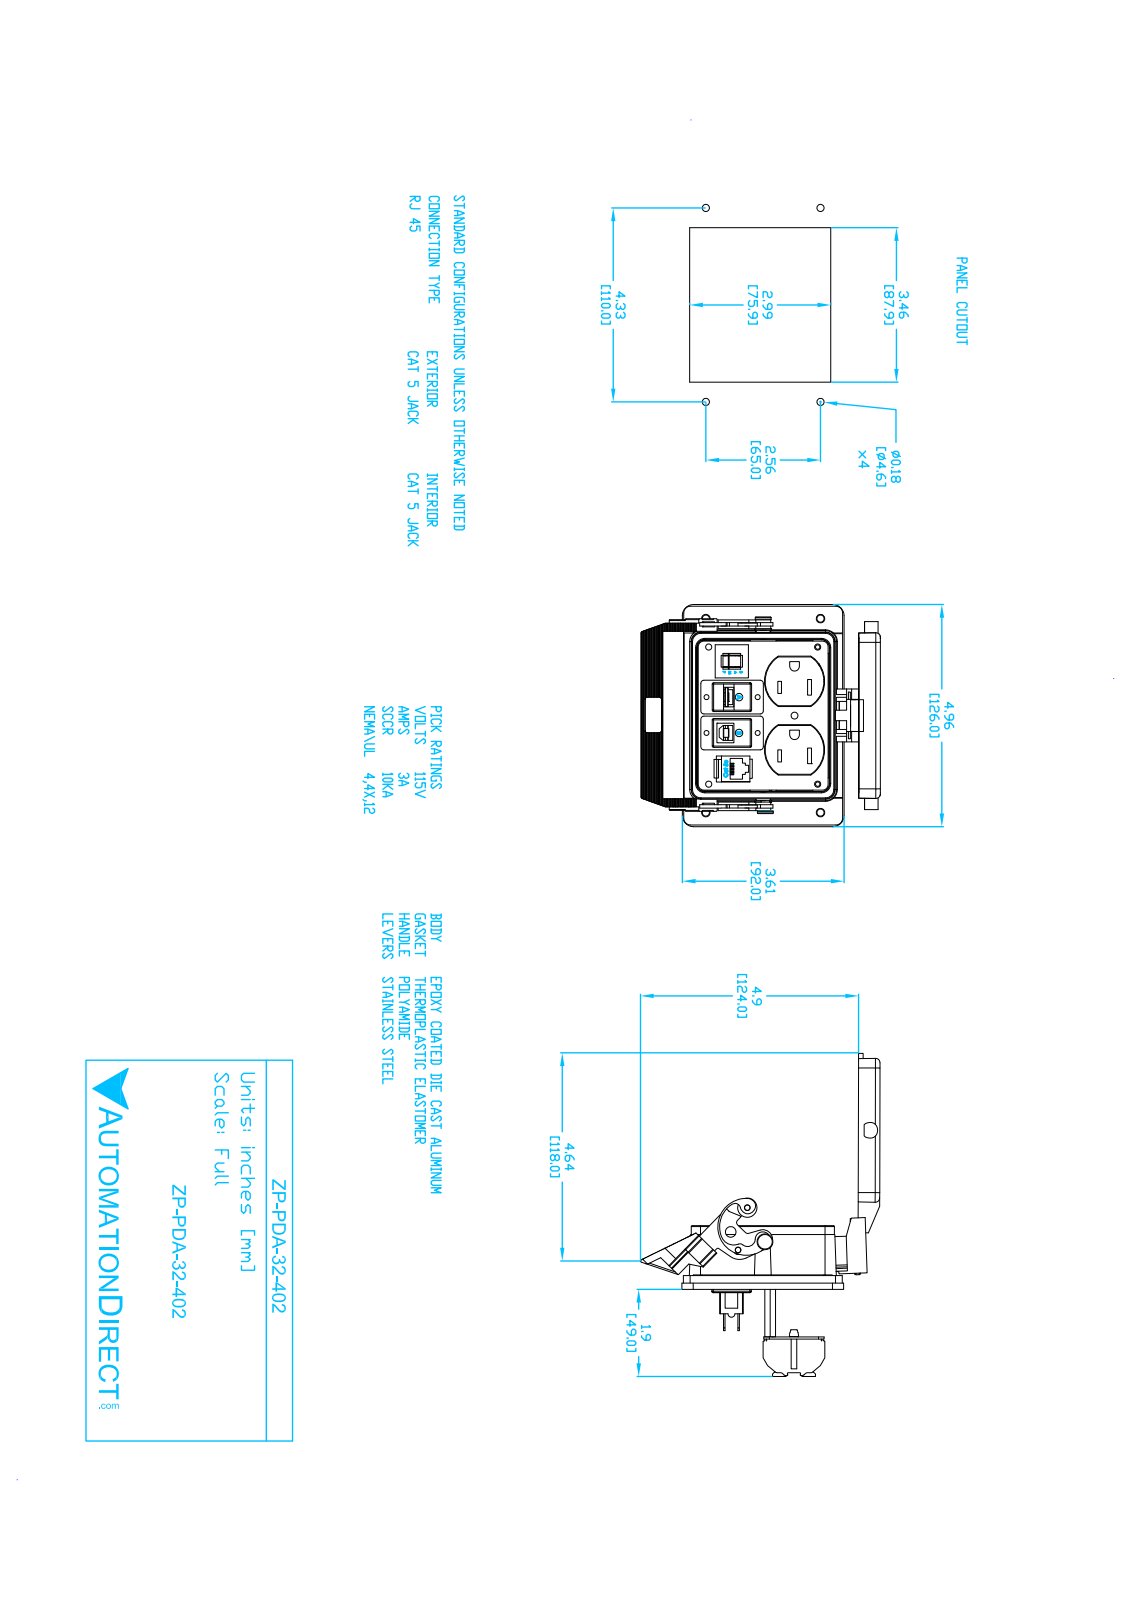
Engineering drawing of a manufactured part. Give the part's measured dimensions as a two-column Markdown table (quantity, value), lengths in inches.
| quantity | value |
| --- | --- |
| part name | ZP-PDA-32-402 |
| STEP written by | SolidWorks 2017 (AUTOMOTIVE_DESIGN) |
| units | inches |
| bodies | 1 solid, 4342 faces (2892 planar, 811 cylindrical, 639 other) |
| overall size | 6.857 × 5.313 × 4.96 |
| volume | 14.13 in³ |
| surface area | 196 in² |
| round holes (diameter × count) | 0.098 × 8, 0.144 × 8, 0.173 × 6, 0.16 × 4, 0.19 × 4, 0.091 × 3, 0.12 × 2, 0.126 × 2, 0.138 × 2, 0.228 × 2, 0.094 × 1, 0.094 × 1 |
| round bosses / shafts (diameter × count) | 0.22 × 6, 0.118 × 6, 0.226 × 4, 0.205 × 3, 0.354 × 2, 0.344 × 2, 0.43 × 1, 0.258 × 1 |
| partial cylindrical surfaces (radius × count) | 0.012 × 48, 0.02 × 30, 0.02 × 22, 0.008 × 20, 0.1 × 18, 0.006 × 16, 0.025 × 12, 0.035 × 12 |
| main face-to-face distances | 0.135, 0.907, 0.847, 0.06, 0.73, 1.577, 1.637, 0.977, 0.247, 0.6 |
| hole center spacings | 0.472, 3.071, 0.236, 0.633, 1.063, 1.287, 1.378, 1.569 |
